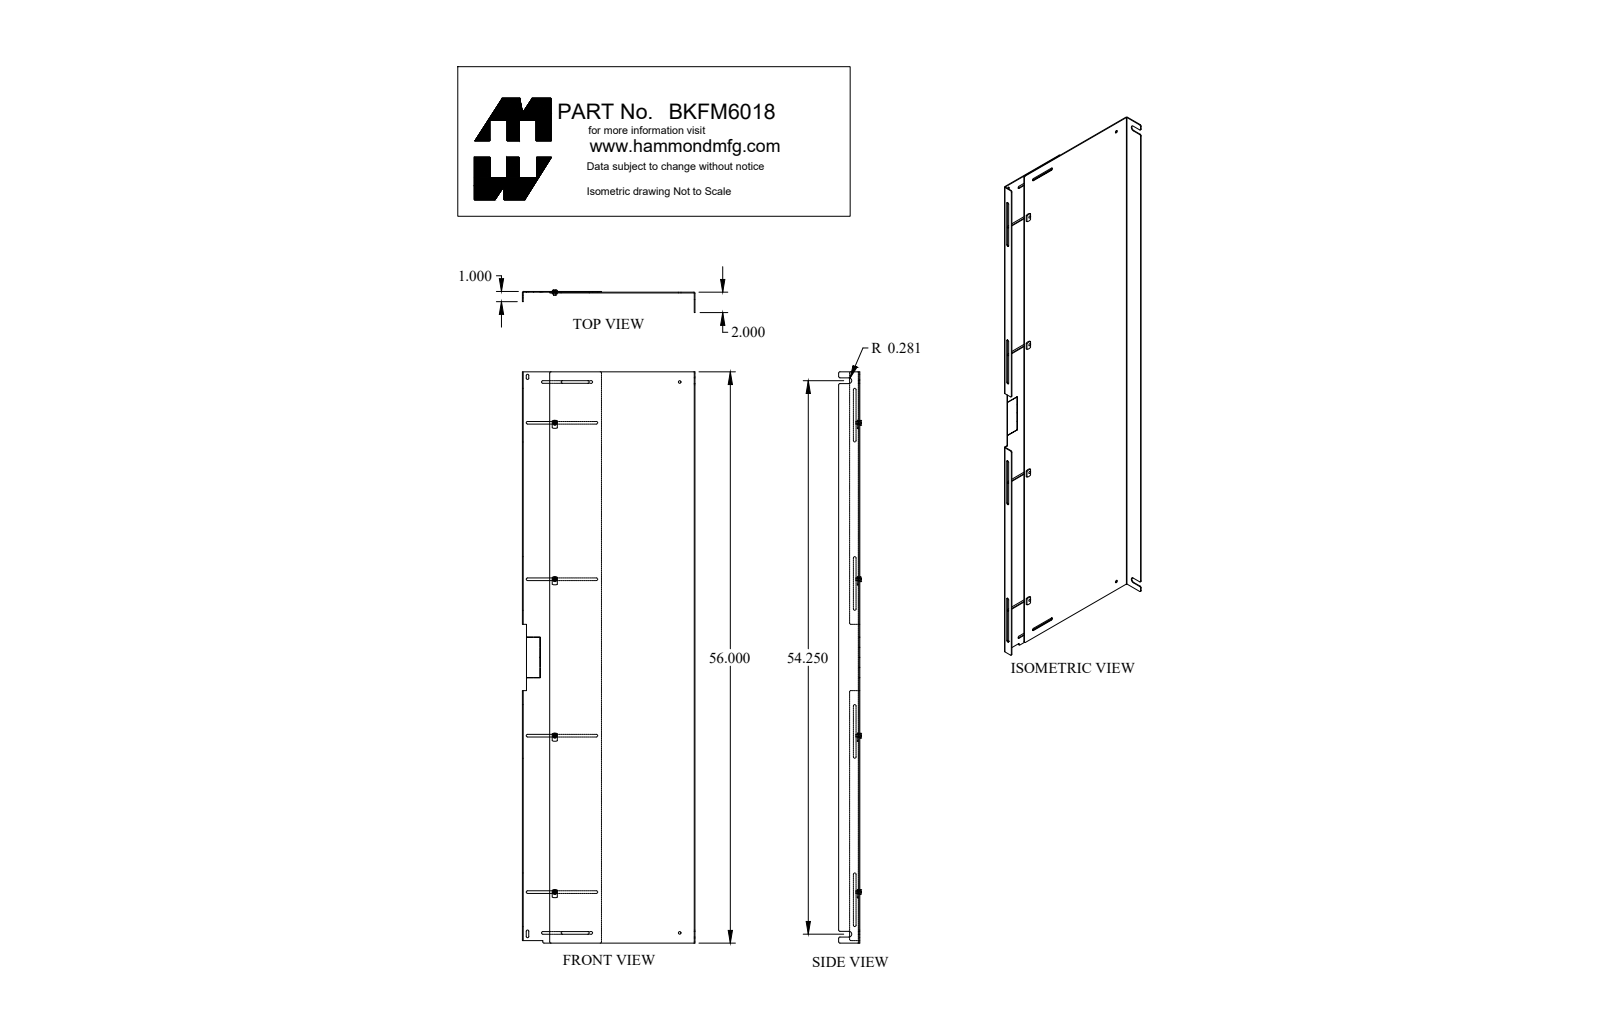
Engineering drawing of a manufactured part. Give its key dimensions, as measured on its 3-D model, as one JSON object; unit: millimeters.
{"part_name": "BKFM6018_Default", "step_written_by": "SolidWorks 2019 (CONFIG_CONTROL_DESIGN)", "units": "millimeters", "bodies": {"solids": 10, "faces": 317, "planar": 158, "cylindrical": 115, "other": 44}, "overall_size": [1422.4, 429.9, 56.8], "volume_mm3": 1610000, "surface_area_mm2": 1781000, "round_holes": [[5.1, 4], [8, 4], [6.6, 2]], "round_bosses_or_shafts": [[11.9, 4], [7.4, 4], [6.4, 4]], "partial_cylinders_radius": [[3.3, 24], [3.2, 19], [12.7, 8], [0.9, 2], [2.7, 2], [7.1, 2]], "face_to_face_distances": [1.8, 3.7, 1.8, 428, 429.9, 426.2, 428, 67.9, 66.1, 360.1], "hole_center_spacings": [327.3, 389.5, 581.4, 778.9, 933.9, 1307.6, 389.5, 1168.4]}
